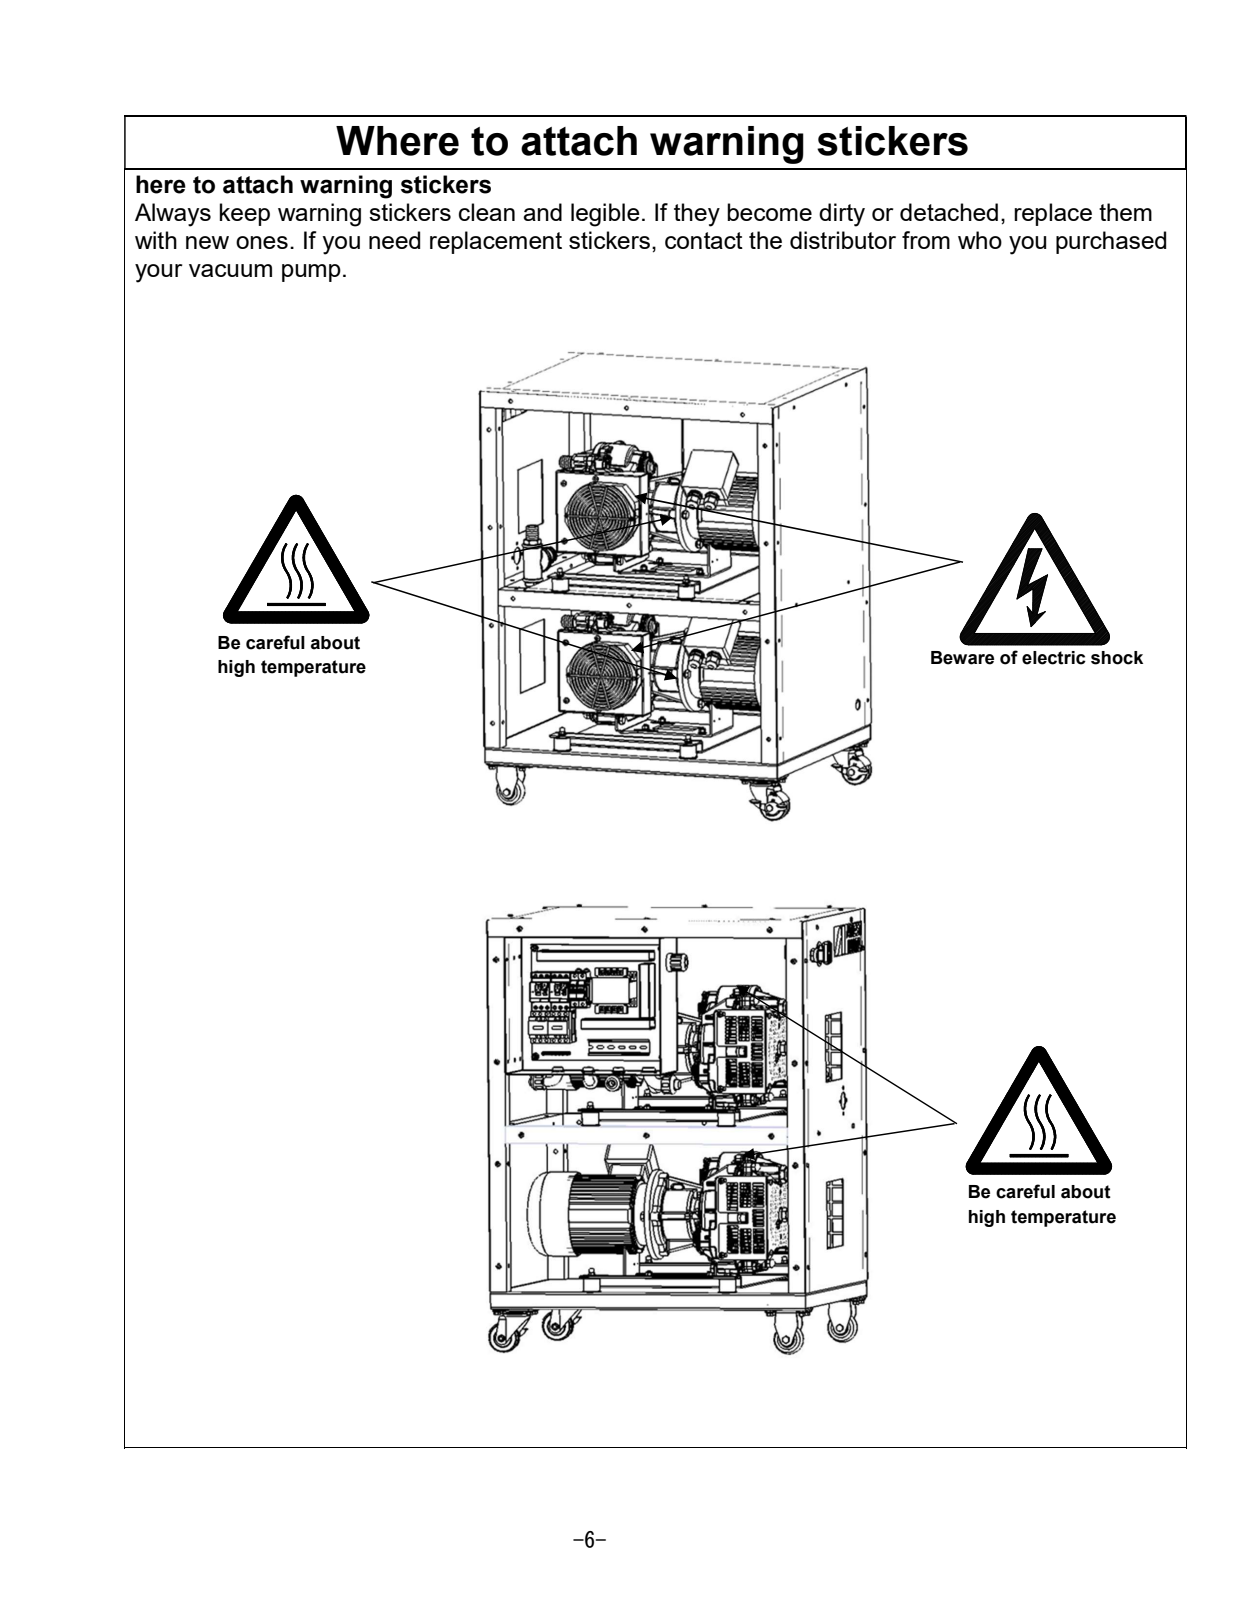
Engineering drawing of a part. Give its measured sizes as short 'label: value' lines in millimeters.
name: GVSU-1000 AP203
written by: SolidWorks 2017 (CONFIG_CONTROL_DESIGN)
unit: mm
bodies: 0 solids, 1778 faces (1225 planar, 236 cylindrical, 317 other)
size: 979.43 × 779.3 × 600.12
holes: 8× ⌀9, 5× ⌀20, 4× ⌀4.58, 4× ⌀6, 3× ⌀21.41, 2× ⌀53.77, 1× ⌀18, 1× ⌀25, 1× ⌀32, 1× ⌀33.02
bosses: 20× ⌀17.86, 5× ⌀40, 4× ⌀35, 3× ⌀7.94, 2× ⌀62.79, 2× ⌀58.83, 2× ⌀20.32, 2× ⌀8
rounds: 17× R5, 10× R3, 9× R3.96, 8× R6.35, 8× R9.65, 7× R2.54, 6× R4.29, 4× R3.81
face distances: 1.6, 577.8, 731.6, 576.2, 38.1, 579.4, 838.1, 3.55, 39.7, 730
hole spacings: 24, 33.94, 21.62, 48, 100, 141, 172.86, 196.46
